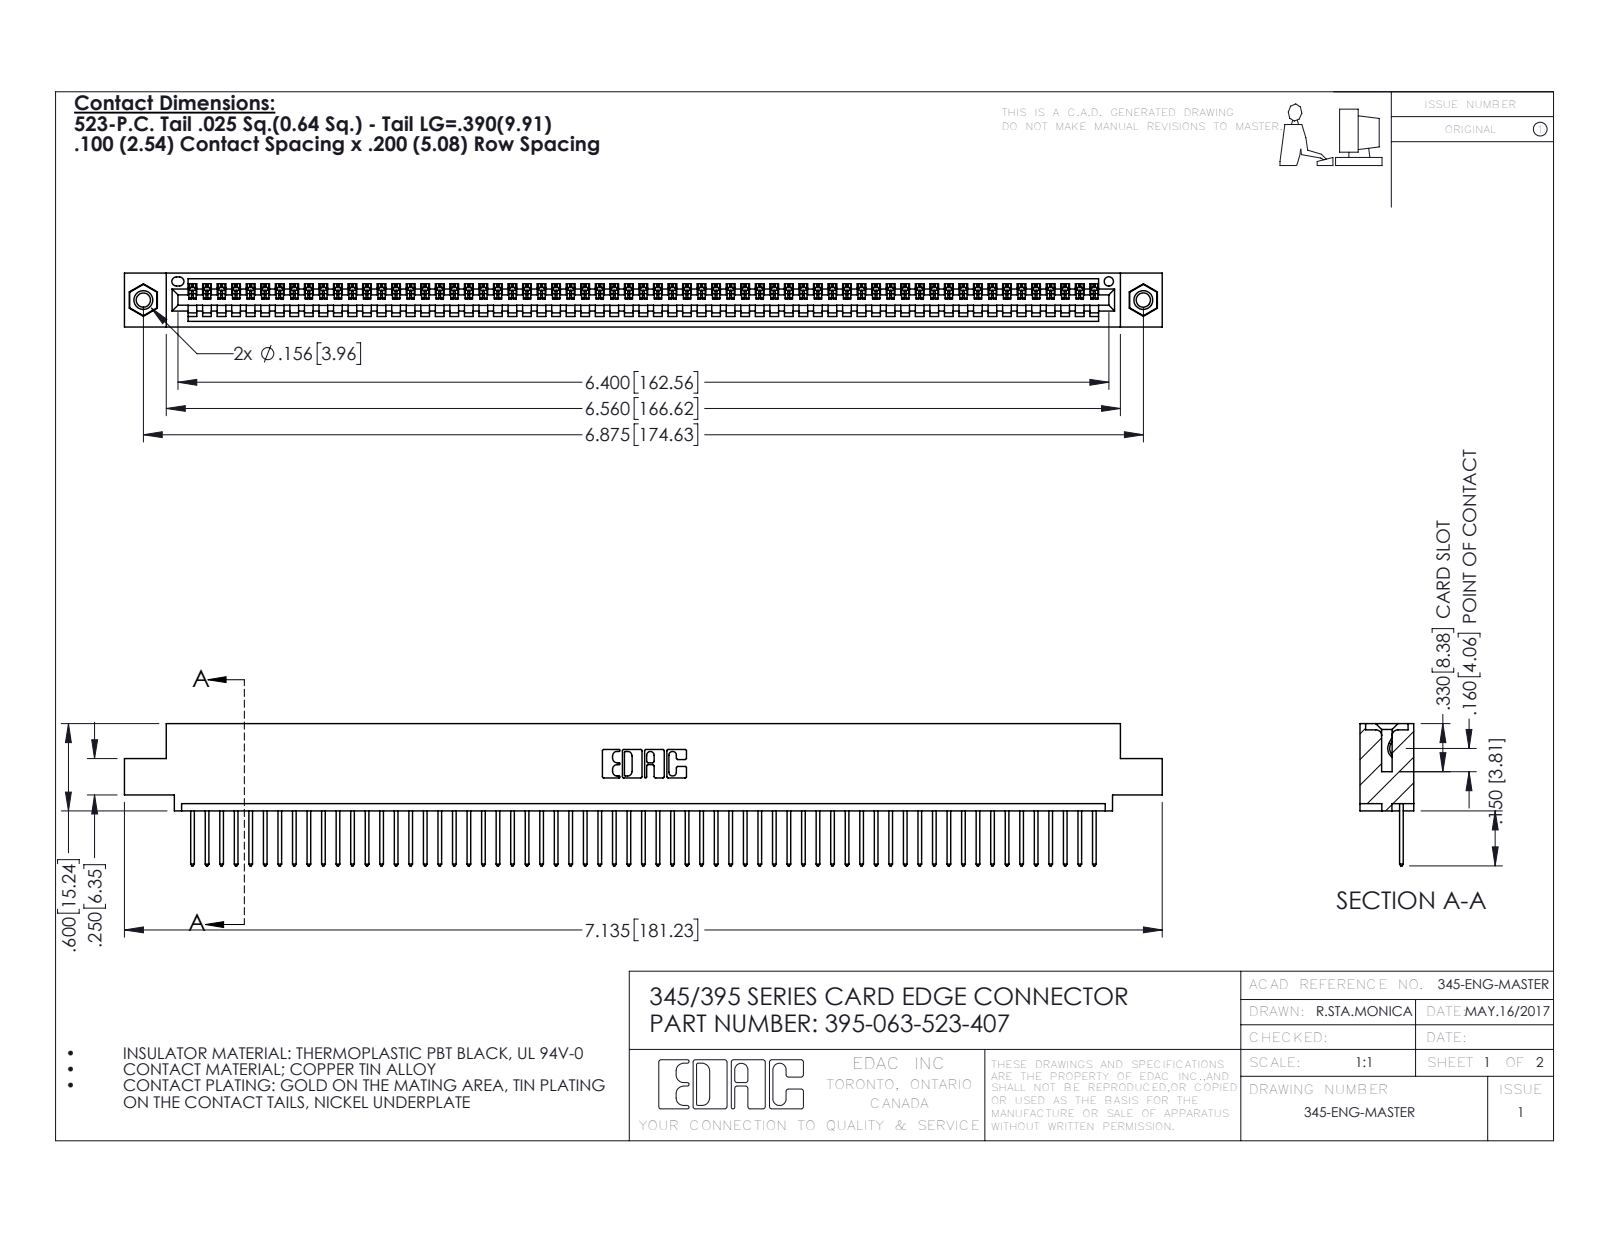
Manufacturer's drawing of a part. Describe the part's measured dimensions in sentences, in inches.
The part is named "345-292-001_345-293-123; 345-250-001_345-250-005-103; 395-063-523-407; 345 Part_0.110 Offset - 0.156 Dia-TI". Its 3-D file was written by "SolidWorks 2016 (CONFIG_CONTROL_DESIGN)". It is 66 solids with 3844 faces: 2636 planar, 1192 cylindrical and 16 other. Overall it measures 7.135 by 0.977 by 0.37 inches. Its volume is 1.054 cubic inches and its surface area 36.31 square inches. Round holes: 2 of diameter 0.098, 2 of diameter 0.125, 2 of diameter 0.156, 1 of diameter 0.064. Round bosses or shafts: 2 of diameter 0.155. Partial cylindrical surfaces (rounded edges, fillets, slot ends): 126 of radius 0.006, 126 of radius 0.01, 22 of radius 0.01, 6 of radius 0.007, 6 of radius 0.031, 3 of radius 0.026, 2 of radius 0.031, 2 of radius 0.04. The main face-to-face distances are 0.072, 0.298, 0.37, 0.2, 0.098, 0.272, 0.025, 0.225, 0.149, 0.072. The hole center spacings are 0.27, 6.639, 6.875.
